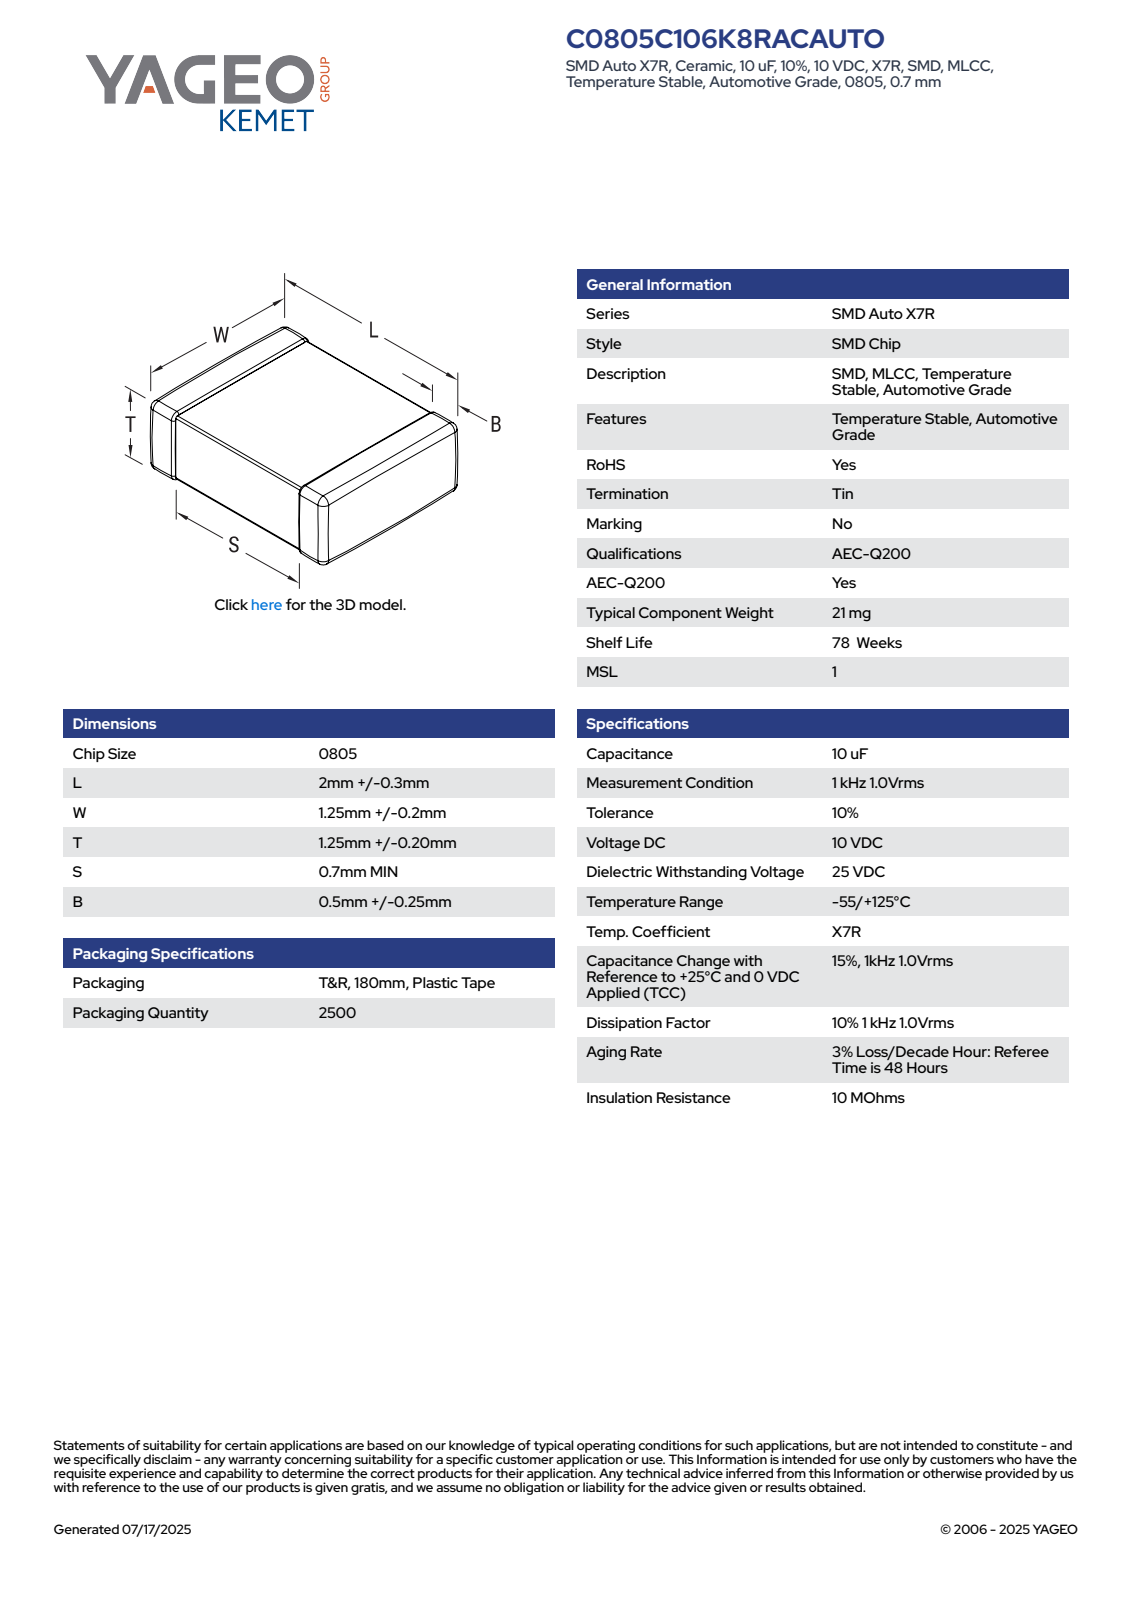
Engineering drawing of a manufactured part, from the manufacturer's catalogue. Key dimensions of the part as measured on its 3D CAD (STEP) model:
Part name (STEP PRODUCT): CCS_CCSTD_0805_L2.3W1.45T1.45B0.5
STEP written by: SolidWorks 2021 (AUTOMOTIVE_DESIGN)
Units: millimetres
Bodies: 4 solids, 125 faces (71 planar, 38 cylindrical, 16 other)
Overall size (bounding box): 2.3 × 1.45 × 1.45
Volume: 5 mm³ · Surface area: 18 mm²
Main face-to-face distances: 1.42, 1.45, 1.39, 2.3, 1.03, 1.27, 1.24, 1.06, 1.15, 0.87
